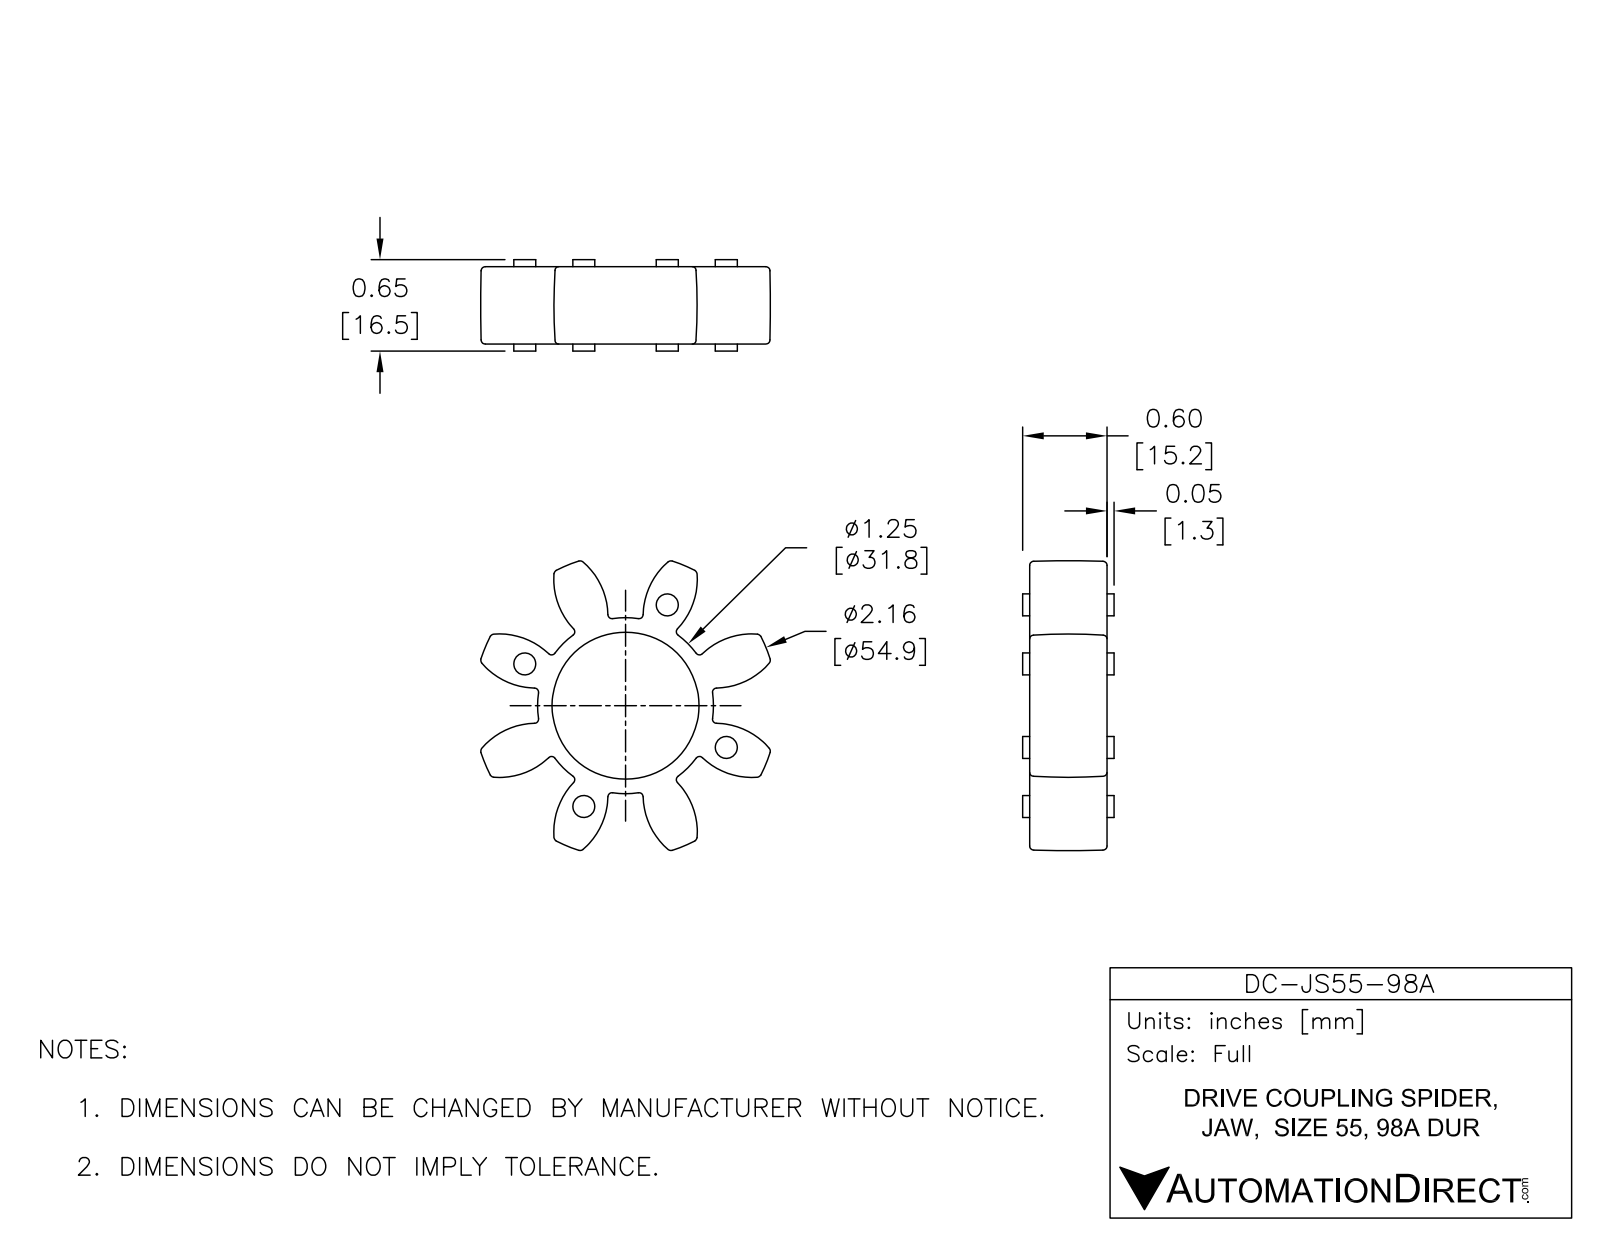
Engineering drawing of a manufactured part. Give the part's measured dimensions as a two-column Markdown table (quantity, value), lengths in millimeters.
| quantity | value |
| --- | --- |
| part name | DC-JS55-98A |
| STEP written by | SolidWorks 2015 (AUTOMOTIVE_DESIGN) |
| units | millimeters |
| bodies | 1 solid, 258 faces (10 planar, 56 cylindrical, 192 other) |
| overall size | 52.11 × 52.11 × 16.51 |
| volume | 12 424 mm³ |
| surface area | 6 712 mm² |
| round holes (diameter × count) | 26.54 × 1 |
| round bosses / shafts (diameter × count) | 3.96 × 8 |
| partial cylindrical surfaces (radius × count) | 0.75 × 32 |
| main face-to-face distances | 13.98, 1.27, 15.25, 16.52 |
